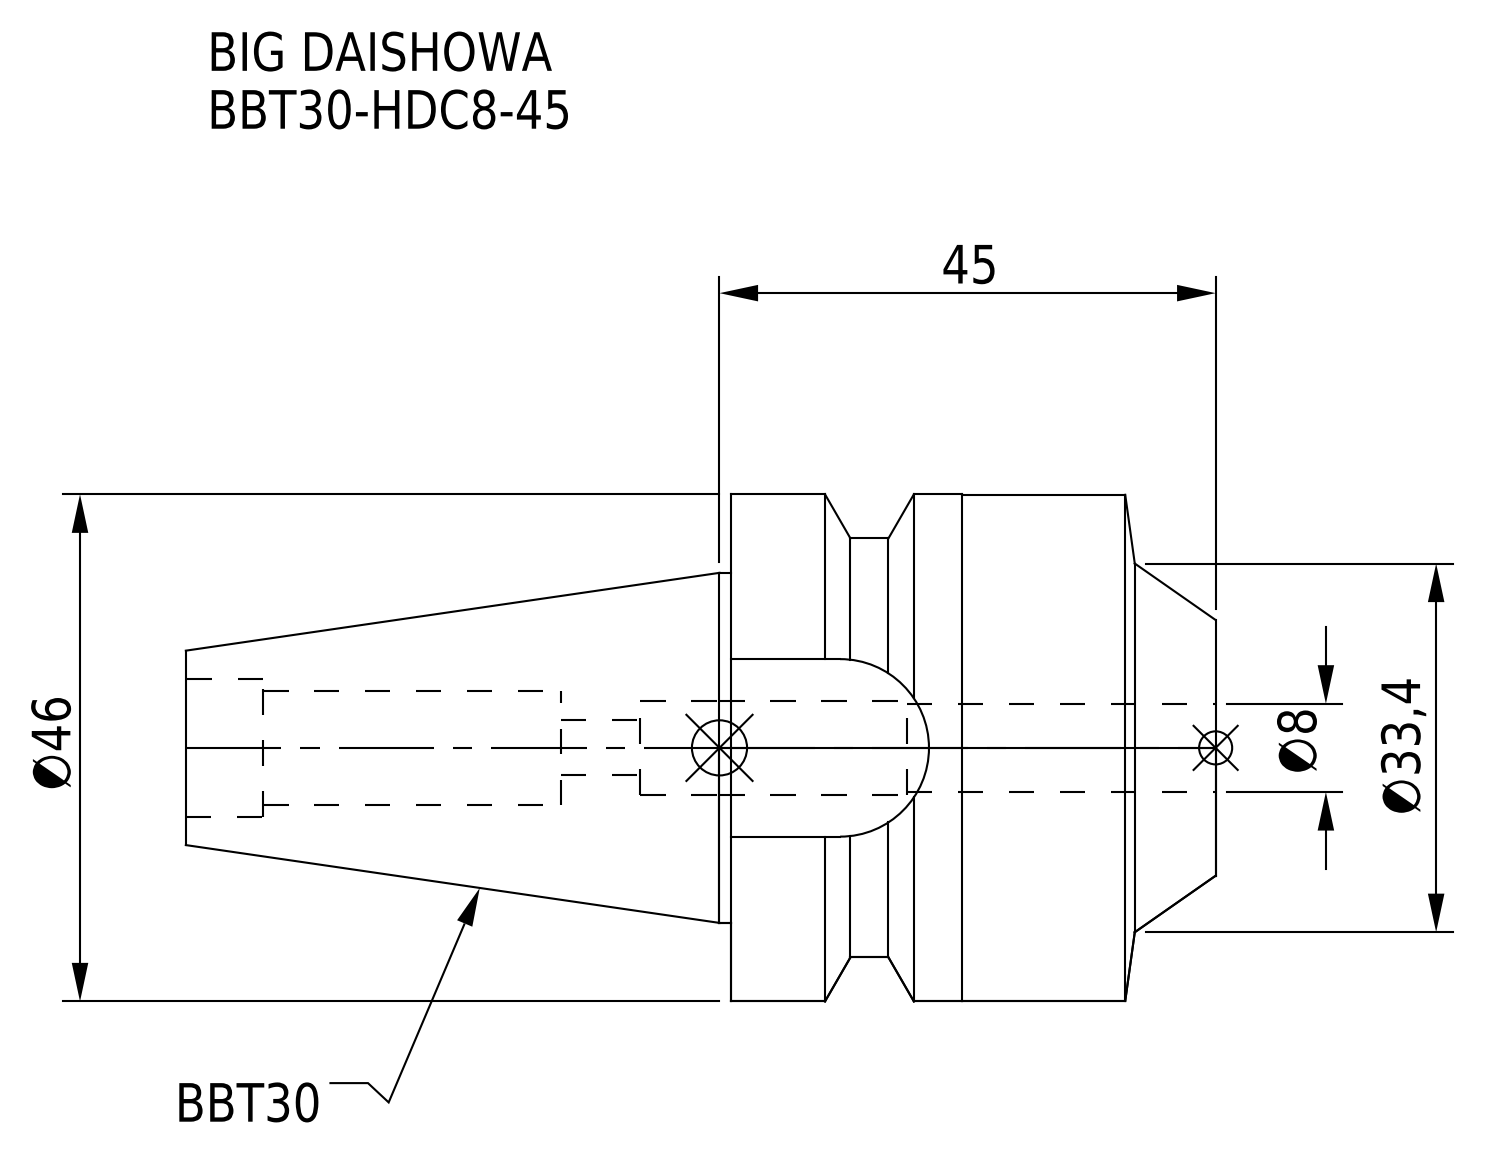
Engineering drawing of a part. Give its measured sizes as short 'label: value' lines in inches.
name: BBT30-HDC8-45
written by: CREO PARAMETRIC BY PTC INC, 2016380 (AUTOMOTIVE_DESIGN)
unit: in
bodies: 1 solid, 48 faces (14 planar, 24 cylindrical, 10 other)
size: 3.677 × 1.811 × 1.811
volume: 4.759 in³; area: 23.72 in²
holes: 1× ⌀0.197, 1× ⌀0.315, 1× ⌀0.335, 1× ⌀0.409, 1× ⌀0.492
bosses: 1× ⌀1.811, 1× ⌀1.807, 1× ⌀1.25
rounds: 1× R0.317, 1× R0.748
face distances: 1.732, 1.283, 3.677, 1.945, 0.634, 2.339, 0.606, 1.339, 3.402, 1.669
